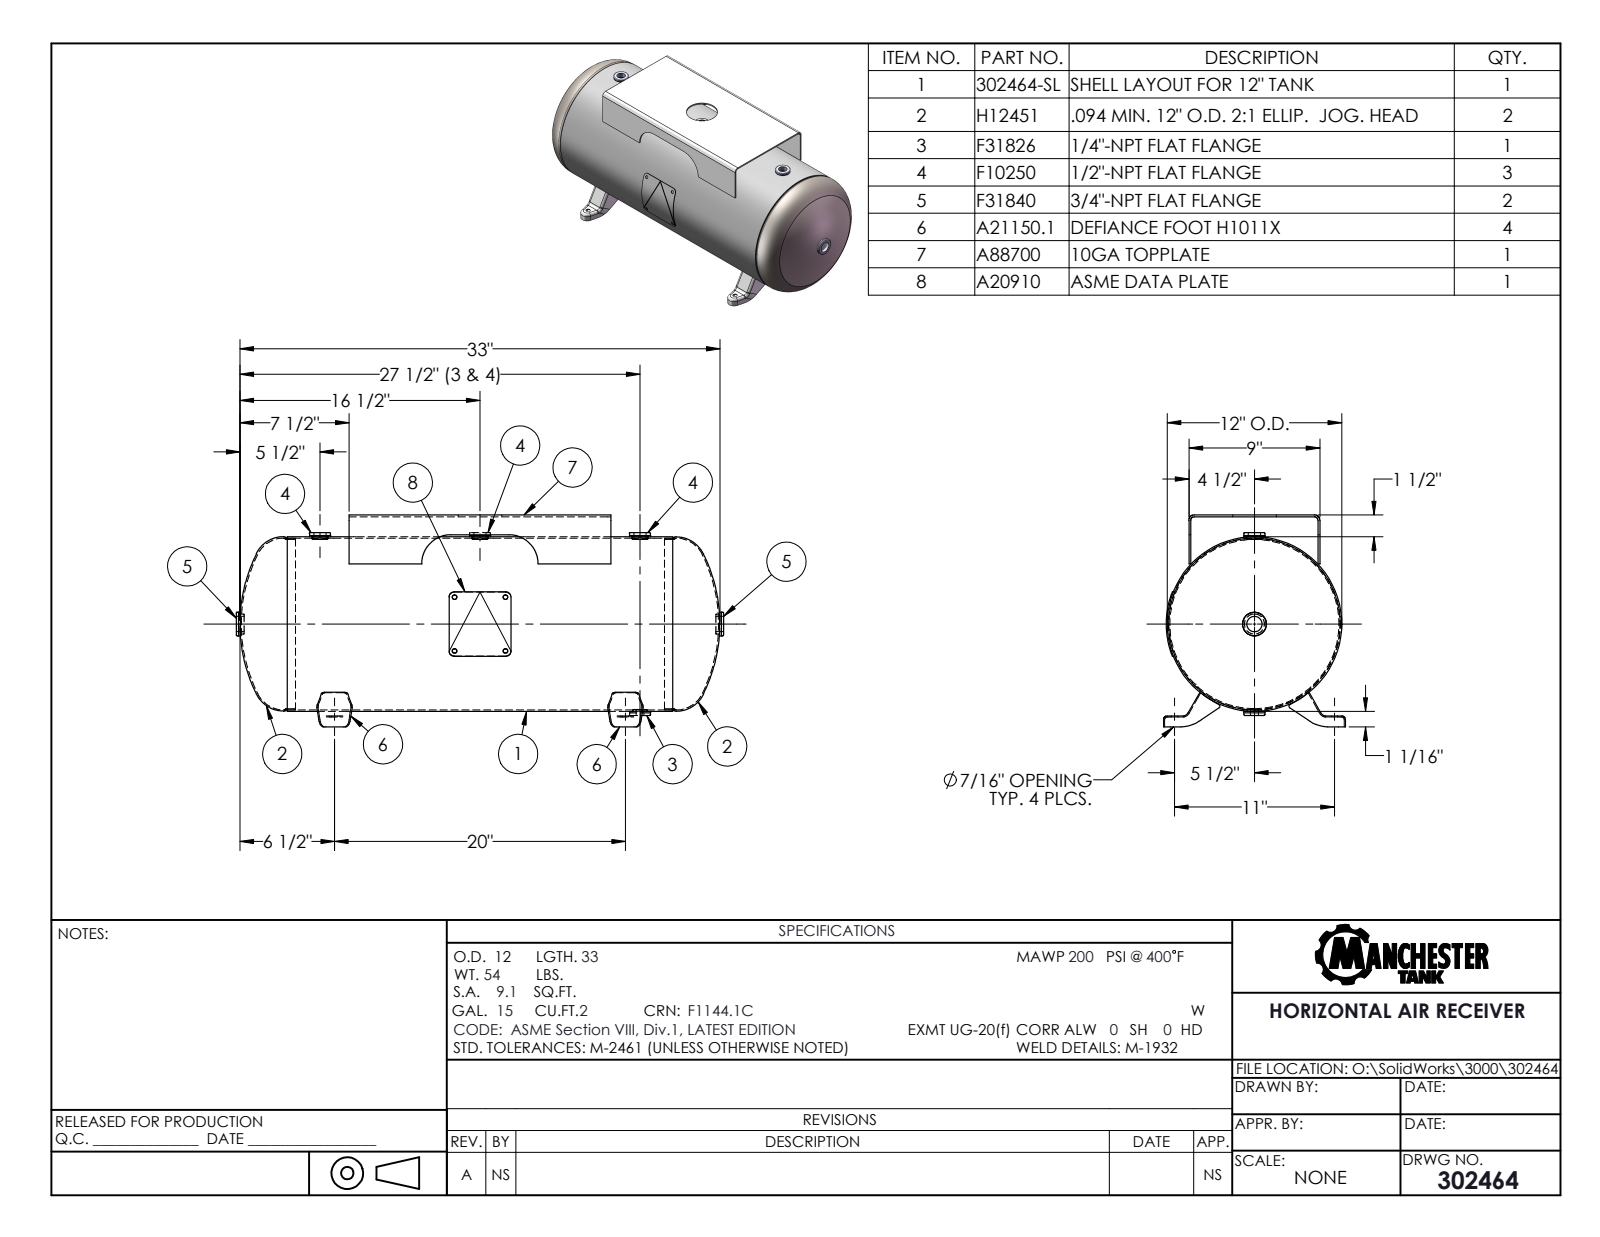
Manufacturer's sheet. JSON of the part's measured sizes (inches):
{"part_name": "302464", "step_written_by": "SolidWorks 2011 (CONFIG_CONTROL_DESIGN)", "units": "inches", "bodies": {"solids": 0, "faces": 359, "planar": 101, "cylindrical": 106, "other": 152}, "overall_size": [34.188, 14.656, 12.5], "round_holes": [[0.437, 4], [0.84, 3], [0.54, 1], [1.05, 1], [3, 1]], "round_bosses_or_shafts": [[1.813, 2], [12, 1], [2.062, 1], [1.5, 1], [1.438, 1]], "partial_cylinders_radius": [[0.25, 12], [0.16, 8], [0.41, 4], [0.5, 4], [0.125, 2], [0.34, 2], [0.384, 2], [1.209, 2]], "face_to_face_distances": [0.134, 0.135, 8.865, 9, 8.731, 0.09, 4.375, 22.375, 19.34, 3.831], "hole_center_spacings": [5.59, 11, 11.413, 21.708, 20, 22.826, 22]}
